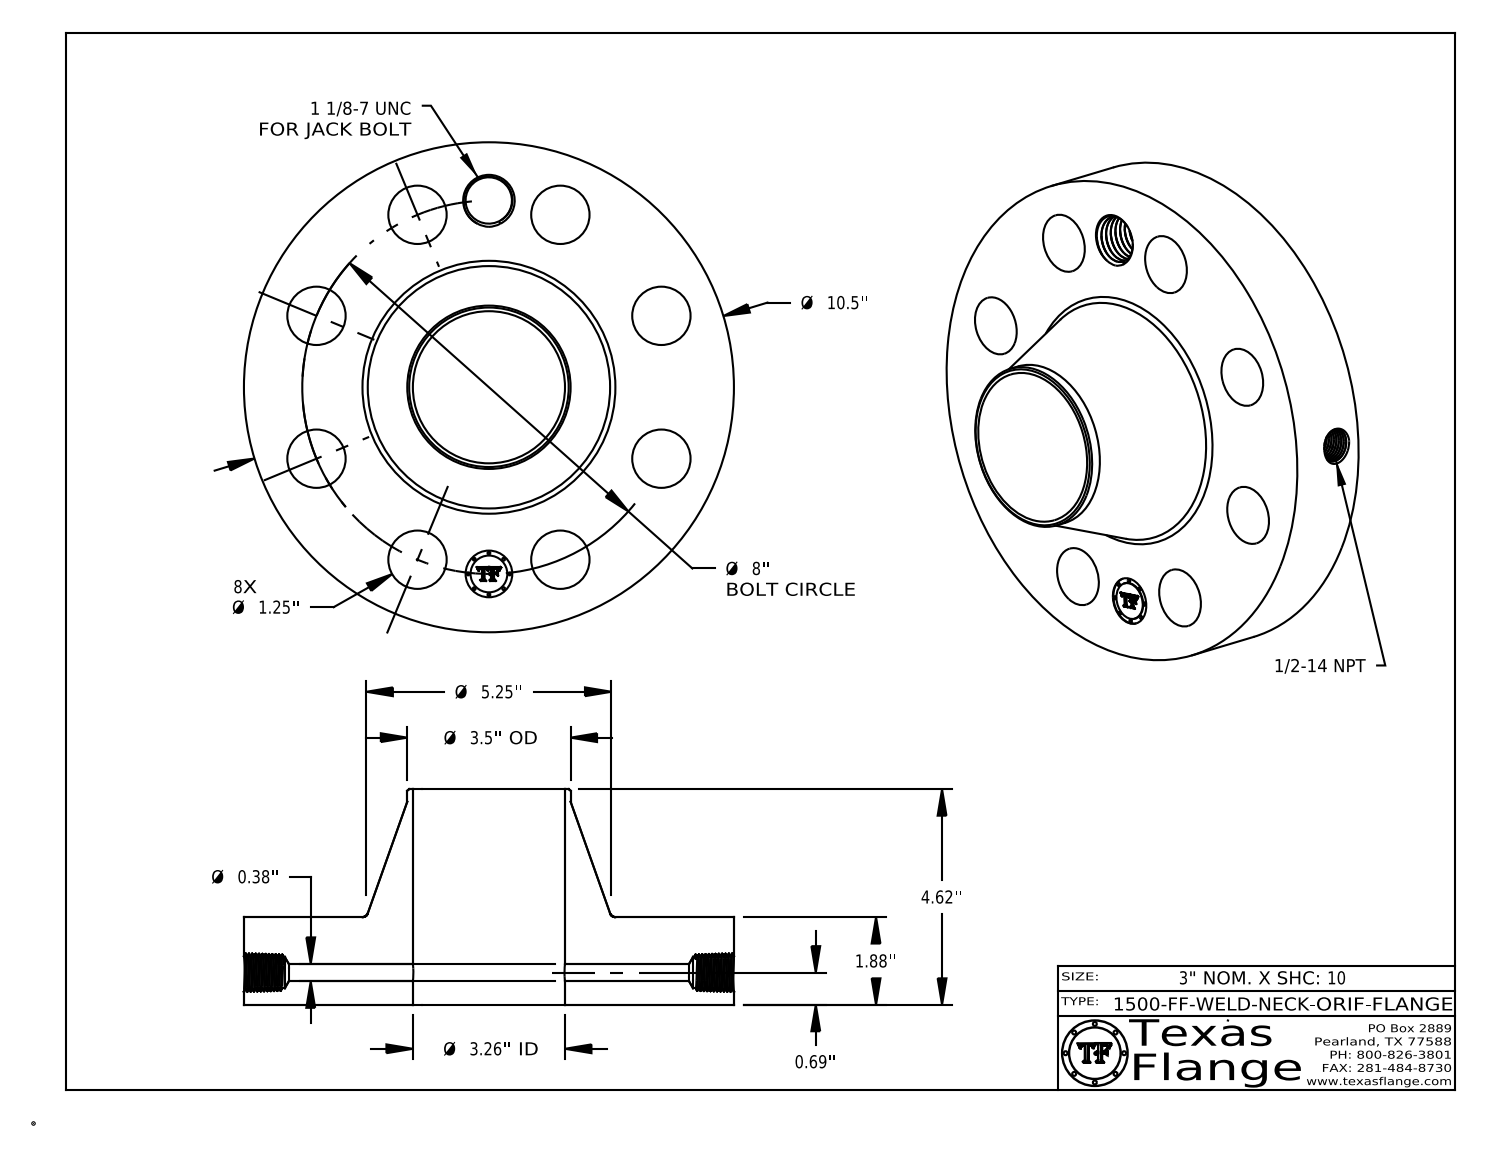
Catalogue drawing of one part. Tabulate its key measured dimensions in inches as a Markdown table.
| quantity | value |
| --- | --- |
| part name | 1500-FF-WELD-NECK |
| STEP written by | CATIA V5 STEP AP214 (AUTOMOTIVE_DESIGN) |
| units | inches |
| bodies | 1 solid, 757 faces (368 planar, 88 cylindrical, 301 other) |
| overall size | 10.5 × 10.5 × 4.62 |
| volume | 143 in³ |
| surface area | 351.6 in² |
| round holes (diameter × count) | 1.25 × 8, 0.375 × 1, 0.672 × 1, 0.984 × 1, 1 × 1, 3.26 × 1 |
| round bosses / shafts (diameter × count) | 0.061 × 8, 10.5 × 1, 3.5 × 1, 0.788 × 1 |
| main face-to-face distances | 1.88, 4.62, 2.74, 1.865, 0.015, 2.755, 0.298, 0.293, 0.054, 0.248 |
| hole center spacings | 4, 5.657, 7.391, 1.561, 3.061, 3.062, 4.445, 6.652 |
